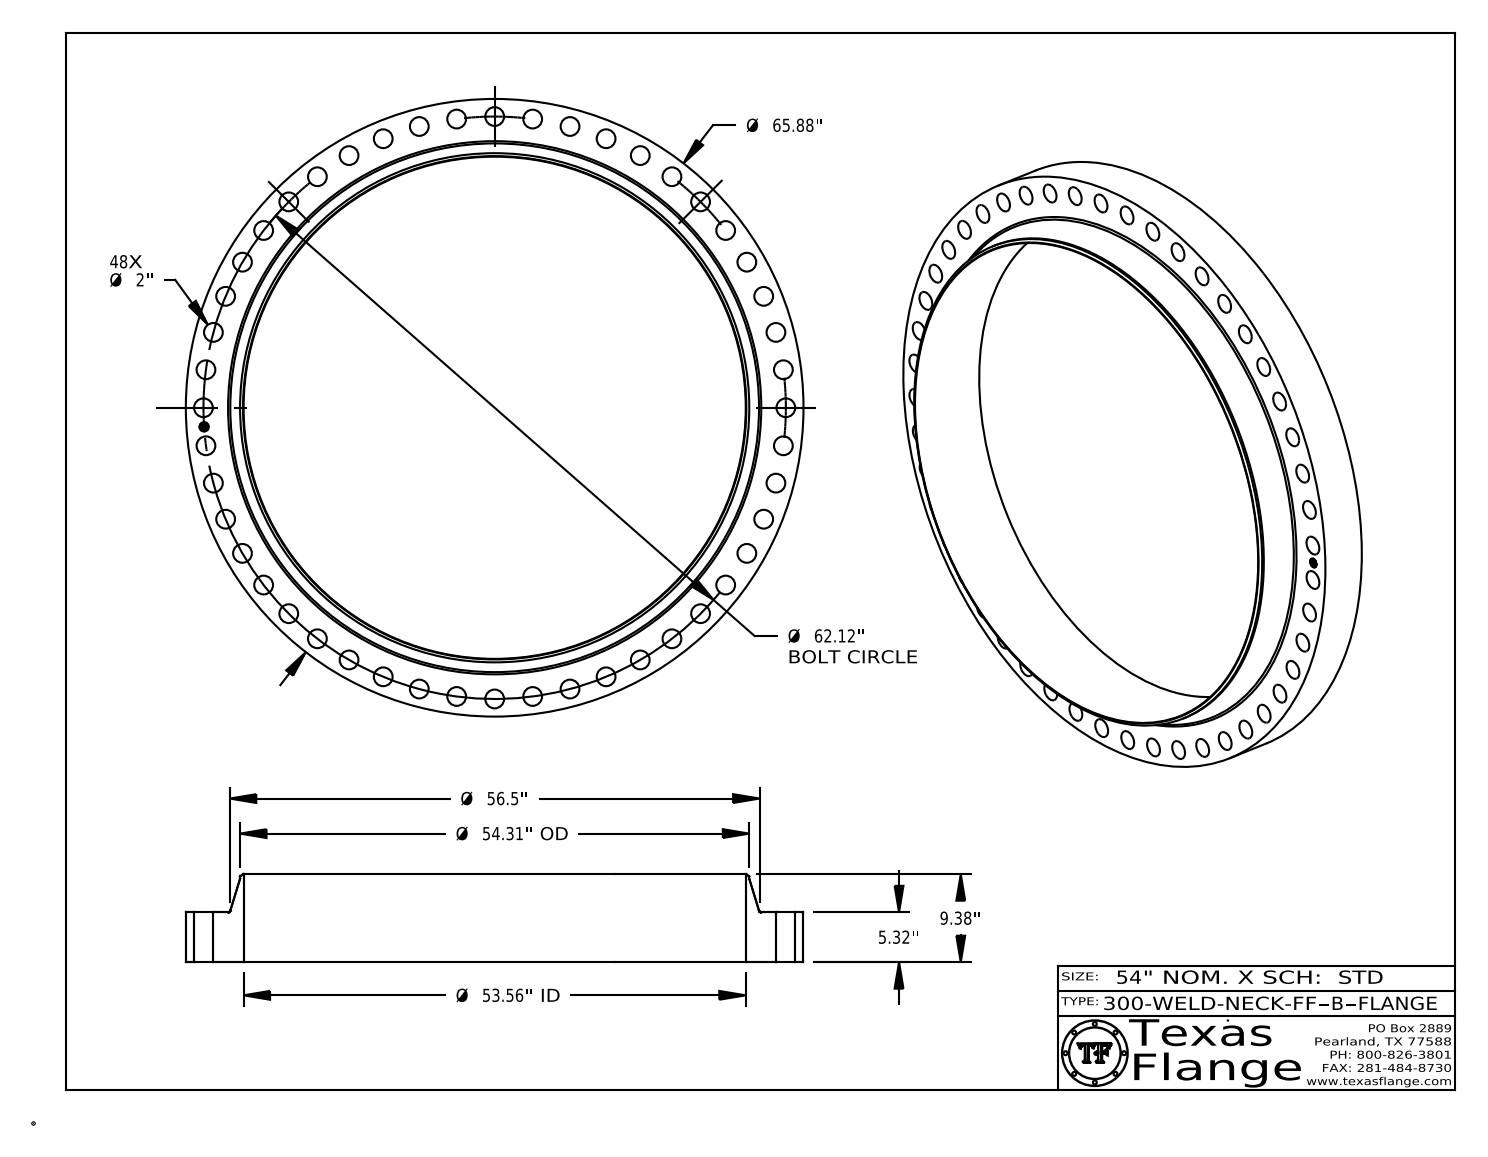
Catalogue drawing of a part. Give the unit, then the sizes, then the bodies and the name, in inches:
Units: inches
Overall size (bounding box): 65.88 × 65.88 × 9.38
Round holes (diameter × count): ⌀2 ×48, ⌀1 ×1, ⌀53.56 ×1
Round bosses / shafts (diameter × count): ⌀0.061 ×8, ⌀65.88 ×1, ⌀54.31 ×1, ⌀0.788 ×1
Main face-to-face distances: 5.32, 9.38, 4.06, 0.015, 5.305, 4.075, 0.298, 0.293, 0.019, 0.054
Hole centre spacings: 31.06, 8.108, 4.063, 58.823, 60.926, 60.003, 19.968, 55.714
Volume: 5 938 in³ · Surface area: 6 801 in²
Bodies: 1 solid, 496 faces (368 planar, 122 cylindrical, 6 other)
Part name (STEP PRODUCT): 300-WELD-NECK-FF, Series B
STEP written by: CATIA V5 STEP AP214 (AUTOMOTIVE_DESIGN)
